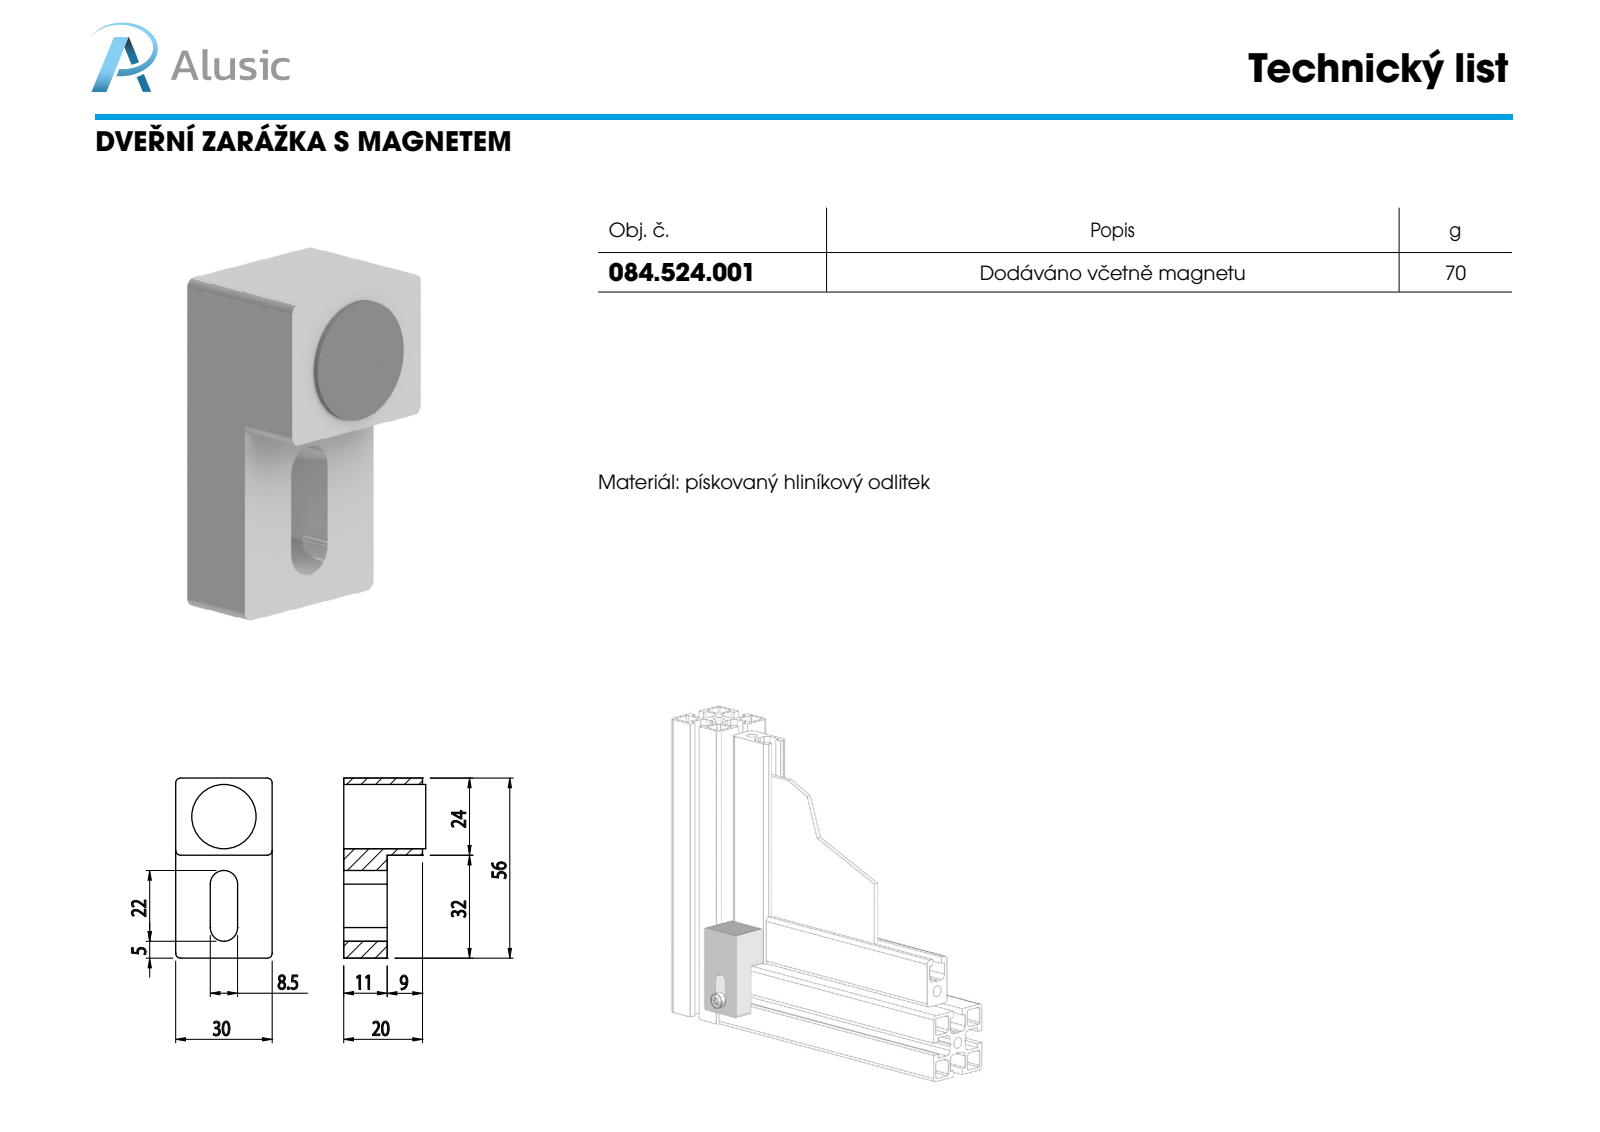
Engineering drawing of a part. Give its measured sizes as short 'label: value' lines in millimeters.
name: 084.524.001
written by: SolidWorks 2011 (CONFIG_CONTROL_DESIGN)
unit: mm
bodies: 1 solid, 22 faces (11 planar, 11 cylindrical, 0 other)
size: 56 × 30 × 25.5
volume: 28 552 mm³; area: 7 248 mm²
bosses: 1× ⌀20
rounds: 6× R1.5, 2× R4.25
face distances: 30, 13.5, 24.5, 11, 56, 10.75, 19.25, 25.5, 12, 1
